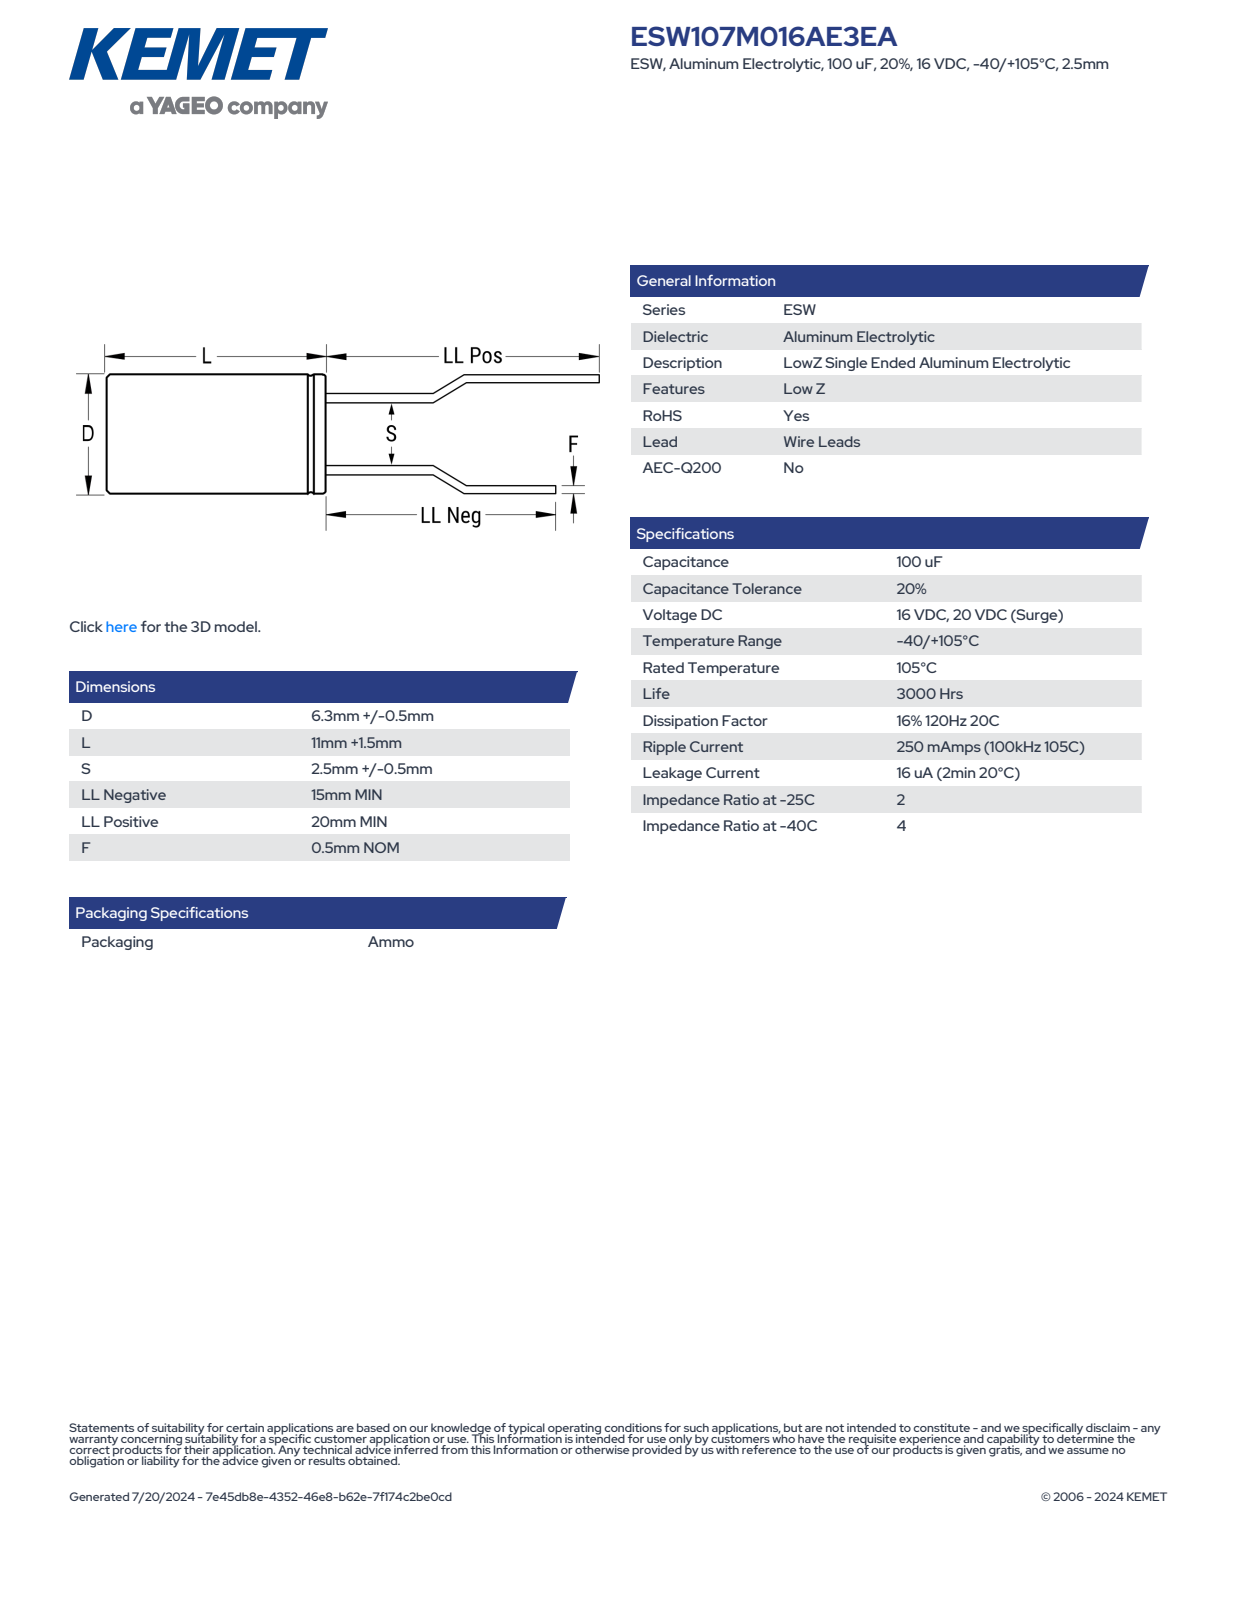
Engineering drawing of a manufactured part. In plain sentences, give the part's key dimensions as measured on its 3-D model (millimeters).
The part is named "CAR_KTRS_6.3X11_D6.8L12.5S2.5F0.5". Its 3-D file was written by "SolidWorks 2014 (AUTOMOTIVE_DESIGN)". It is 4 solids with 73 faces: 61 planar, 8 cylindrical and 4 other. Overall it measures 32.51 by 6.8 by 6.8 millimeters. Its volume is 458 cubic millimeters and its surface area 405 square millimeters. Round bosses or shafts: 2 of diameter 0.5, 1 of diameter 6.8. The main face-to-face distances are 12.5, 12.51, 27.51, 32.51, 27.5, 32.5, 15, 20, 5, 0.8.
